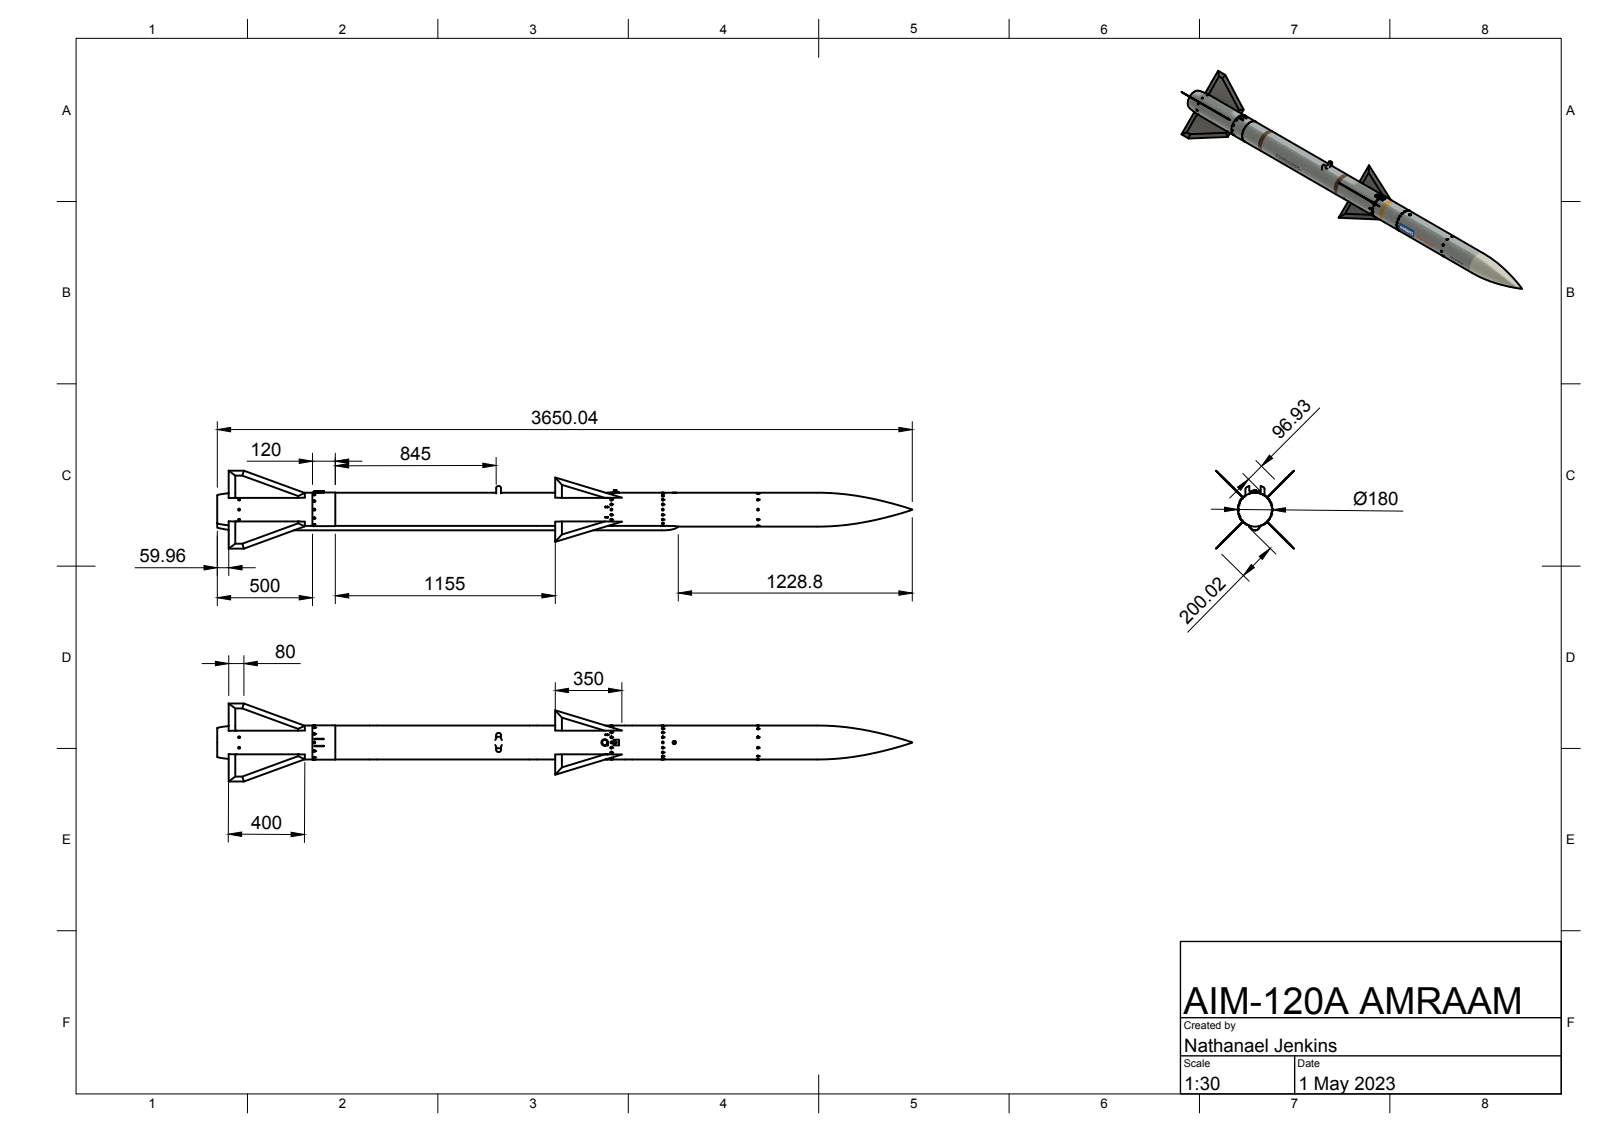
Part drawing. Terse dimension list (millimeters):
name: AIM-120 AMRAAM v18
written by: Autodesk Translation Framework v12.4.0.73 (AUTOMOTIVE_DESIGN)
unit: mm
bodies: 1 solid, 412 faces (53 planar, 123 cylindrical, 236 other)
size: 3650 × 408.71 × 408.71
volume: 87 280 000 mm³; area: 2 670 000 mm²
holes: 1× ⌀20, 1× ⌀27, 1× ⌀35, 1× ⌀130
bosses: 1× ⌀180, 1× ⌀178, 1× ⌀15
rounds: 40× R89, 12× R90, 6× R10, 2× R5, 2× R15
face distances: 3, 10, 50, 37, 13, 47, 2, 1490, 620, 35
hole spacings: 83
